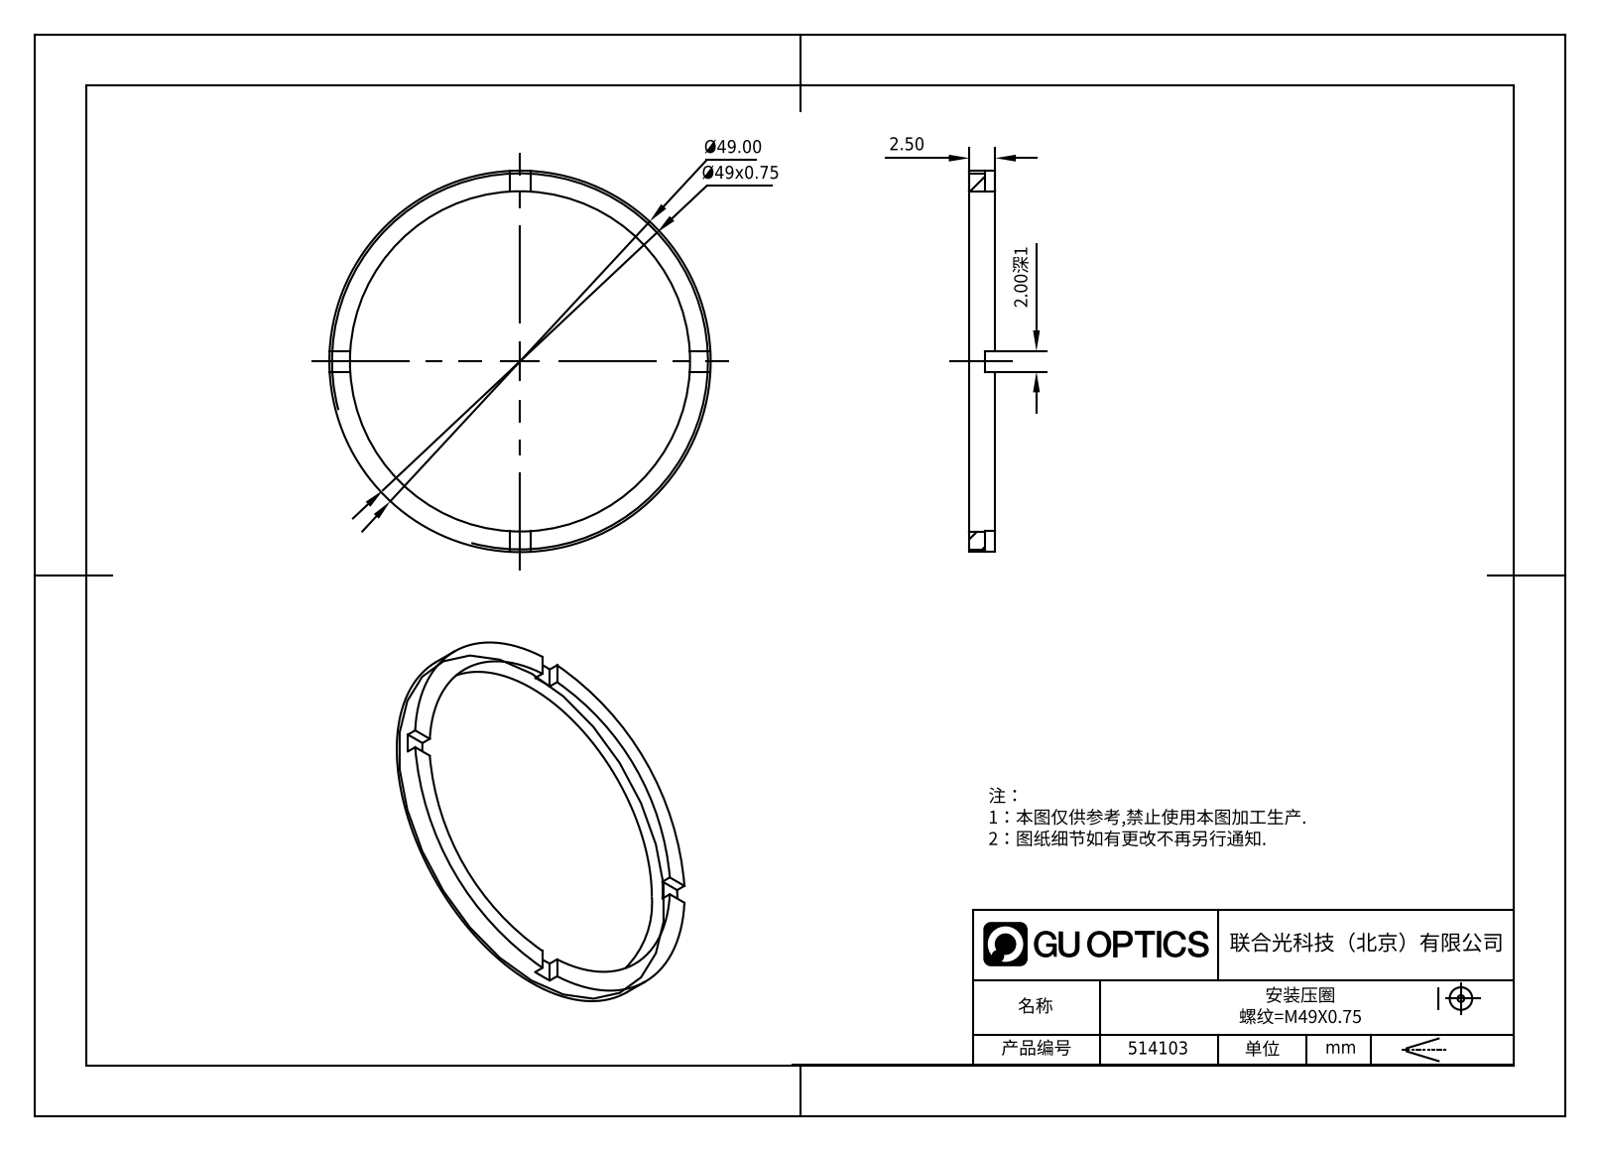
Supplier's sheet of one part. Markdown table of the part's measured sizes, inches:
| quantity | value |
| --- | --- |
| part name | 514103 |
| STEP written by | SolidWorks 2020 (CONFIG_CONTROL_DESIGN) |
| units | inches |
| bodies | 1 solid, 21 faces (17 planar, 4 cylindrical, 0 other) |
| overall size | 1.929 × 1.929 × 0.098 |
| volume | 0.044 in³ |
| surface area | 2.06 in² |
| round holes (diameter × count) | 1.772 × 1 |
| round bosses / shafts (diameter × count) | 1.929 × 1 |
| main face-to-face distances | 0.098, 0.059, 0.039, 0.079 |
